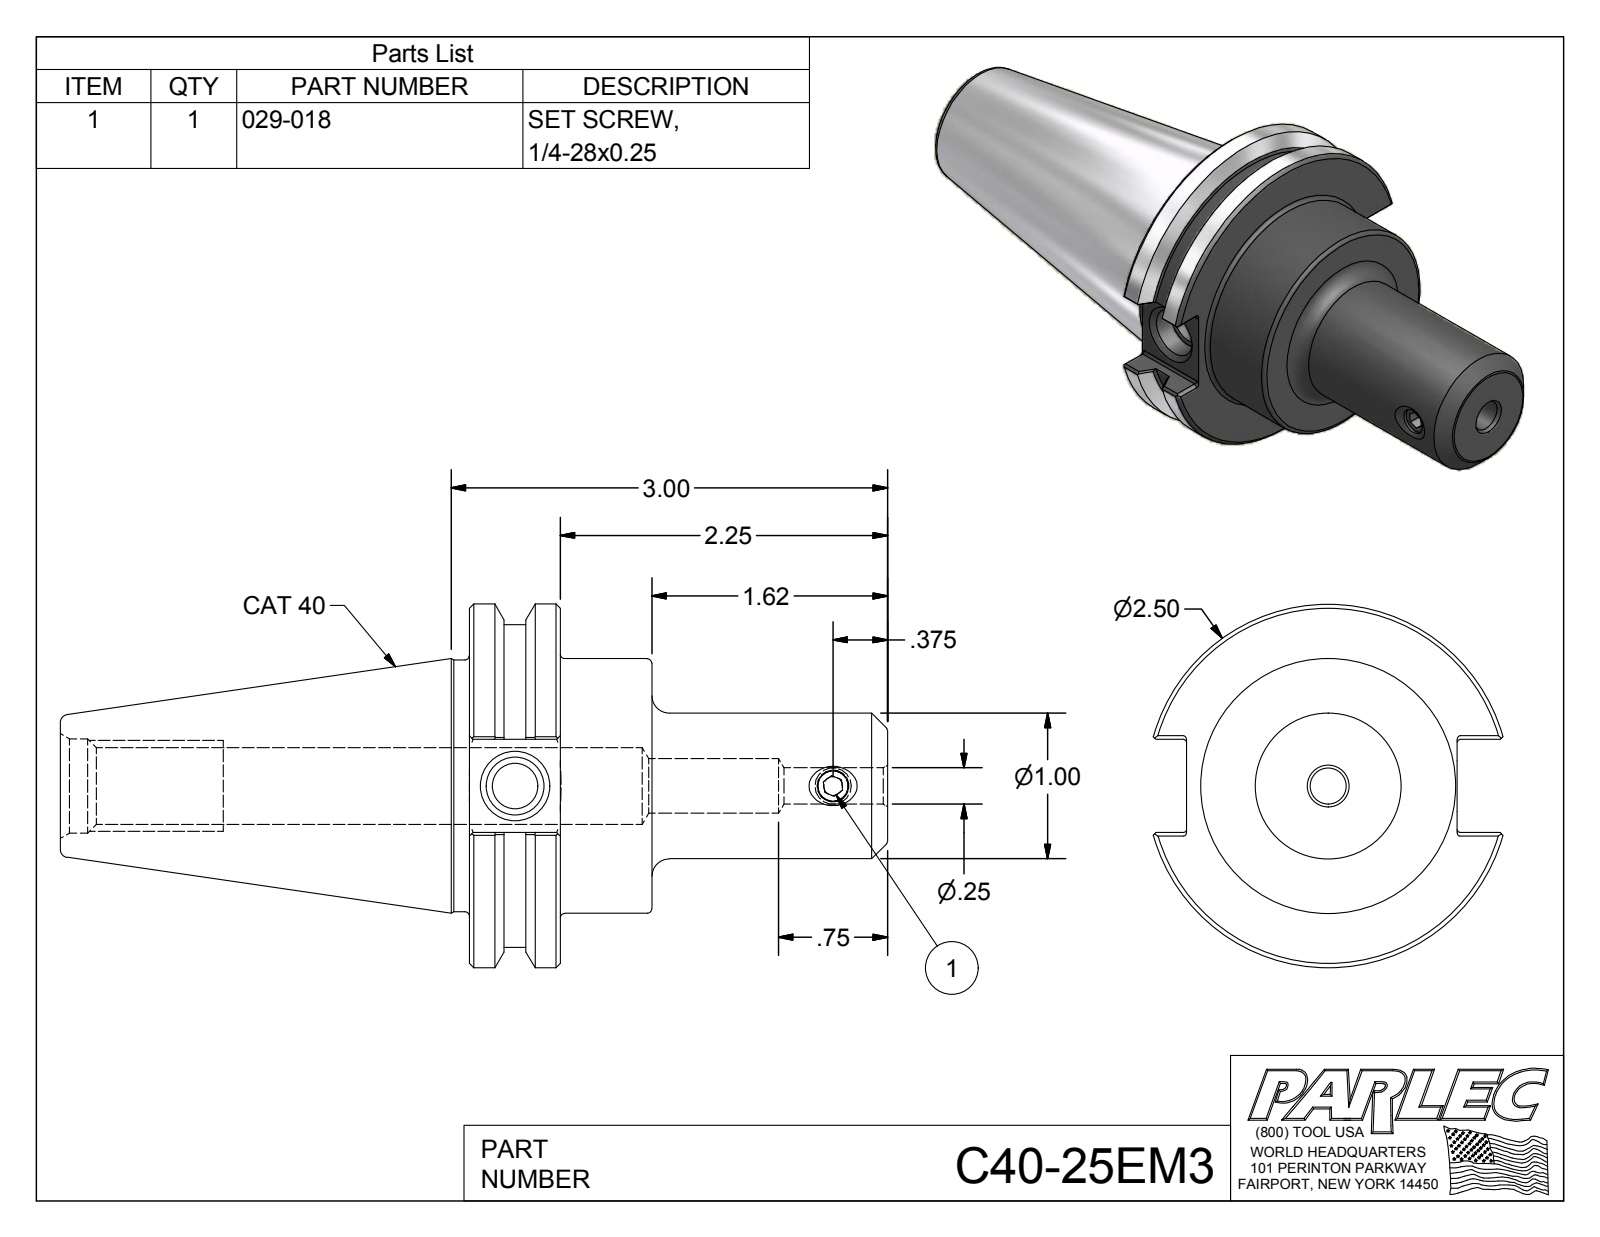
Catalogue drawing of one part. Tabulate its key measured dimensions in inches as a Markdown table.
| quantity | value |
| --- | --- |
| part name | C40-25EM3; C40-25EM3-1; 029-018 |
| STEP written by | Autodesk Inventor 2012 (AUTOMOTIVE_DESIGN) |
| units | inches |
| bodies | 2 solids, 62 faces (20 planar, 16 cylindrical, 26 other) |
| overall size | 5.688 × 2.5 × 2.417 |
| volume | 8.67 in³ |
| surface area | 42.27 in² |
| round holes (diameter × count) | 0.211 × 1, 0.25 × 1, 0.375 × 1, 0.527 × 1, 0.563 × 1, 0.648 × 1 |
| round bosses / shafts (diameter × count) | 2.5 × 1, 2.219 × 1, 1.75 × 1, 1 × 1, 0.25 × 1 |
| main face-to-face distances | 0.625, 1.255, 0.63, 2.875, 2.25, 1.62, 0.64, 2.813, 3.437, 4.067 |
| hole center spacings | 2.185 |
